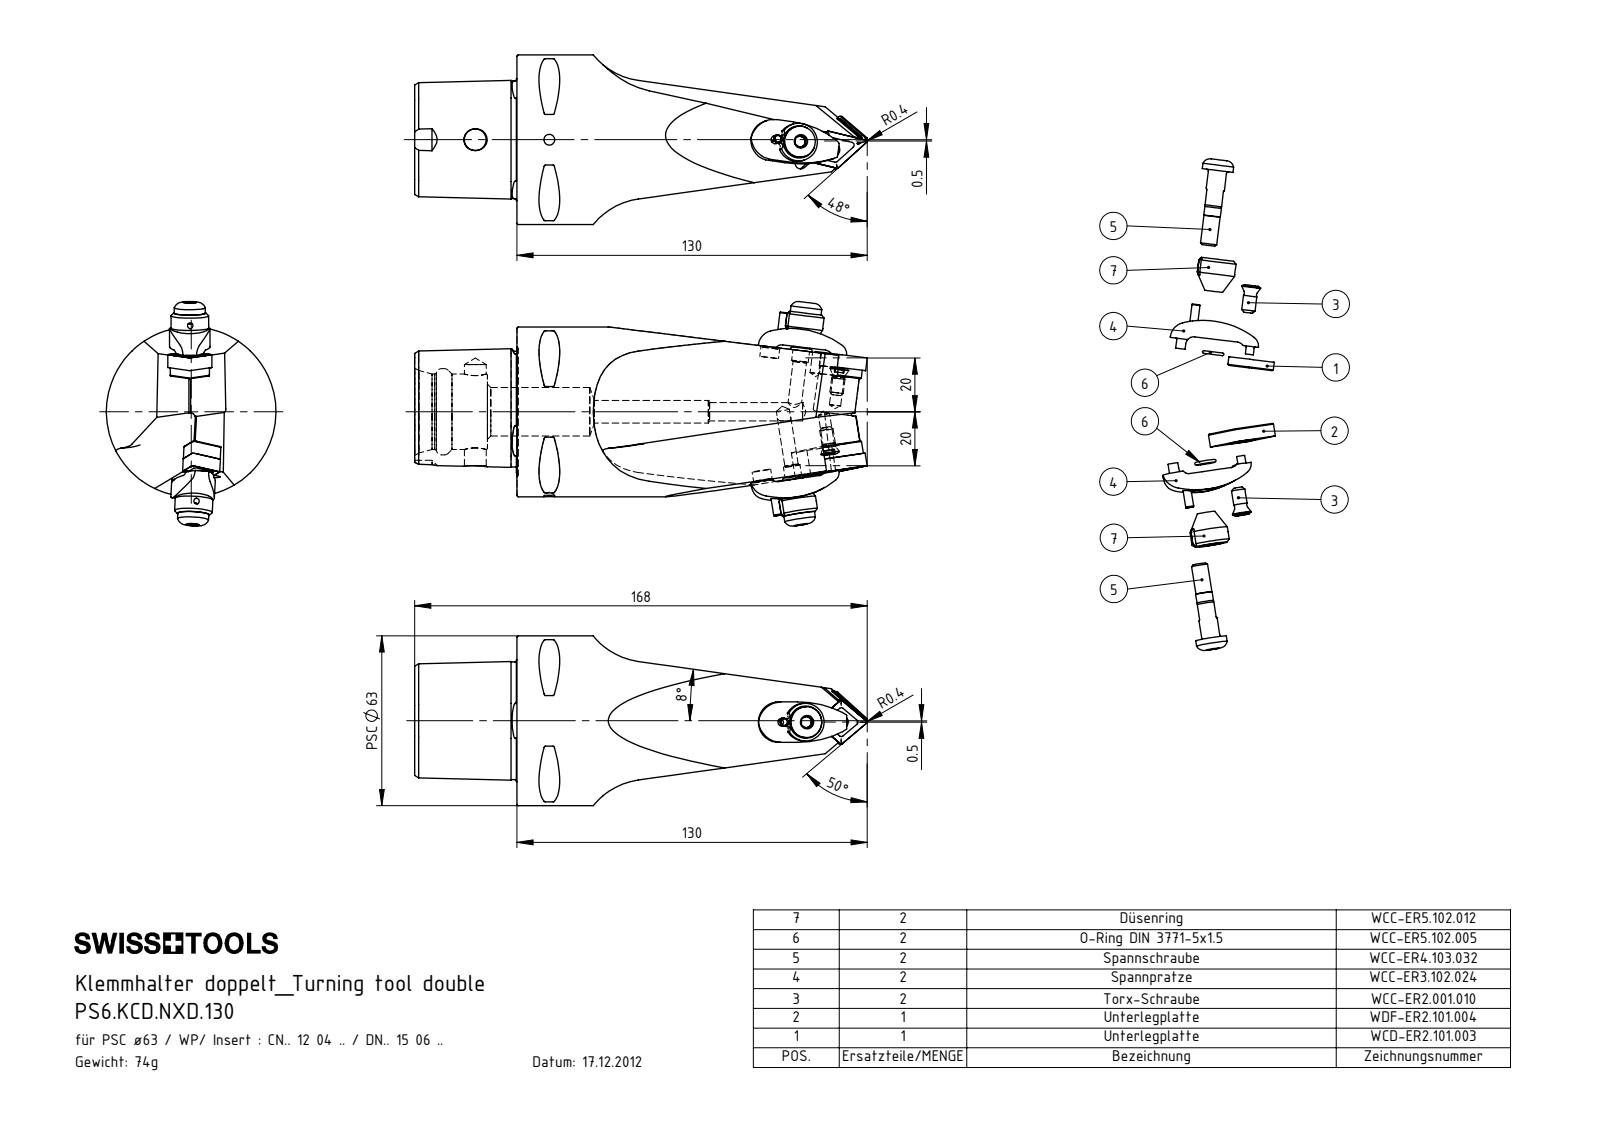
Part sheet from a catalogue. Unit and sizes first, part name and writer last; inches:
Units: inches
Overall size (bounding box): 6.615 × 3.281 × 2.48
Round holes (diameter × count): ⌀0.079 ×6, ⌀0.276 ×4, ⌀0.165 ×3, ⌀0.094 ×2, ⌀0.118 ×2, ⌀0.197 ×2, ⌀0.203 ×2, ⌀0.244 ×2, ⌀0.252 ×2, ⌀0.335 ×2, ⌀0.157 ×1, ⌀0.268 ×1
Round bosses / shafts (diameter × count): ⌀0.118 ×4, ⌀0.551 ×2, ⌀0.453 ×2, ⌀0.276 ×2, ⌀0.268 ×2, ⌀0.244 ×2, ⌀0.236 ×2, ⌀0.197 ×2
Partial cylindrical surfaces — rounded edges, fillets, slot ends (radius × count): R0.015 ×12, R0.016 ×8, R0.02 ×8, R0.039 ×8, R0.027 ×6, R0.027 ×6, R0.059 ×6, R0.079 ×4
Main face-to-face distances: 0.773, 0.5, 0.187, 1.496, 0.227, 0.598, 0.175, 0.411, 0.362, 0.433
Hole centre spacings: 0.315, 0.323, 0.905, 0.582, 0.251, 0.313, 0.566, 0.588
Volume: 17.31 in³ · Surface area: 75.89 in²
Bodies: 17 solids, 489 faces (173 planar, 148 cylindrical, 168 other)
Part name (STEP PRODUCT): ISO 13337 - 3 x 12_PreviewCfg; WCC-ER2.001.010_A; WCC-ER3.102.024_C; WCC-ER5.102.012_B (+8 more)
STEP written by: SolidWorks 2017 (AUTOMOTIVE_DESIGN)
